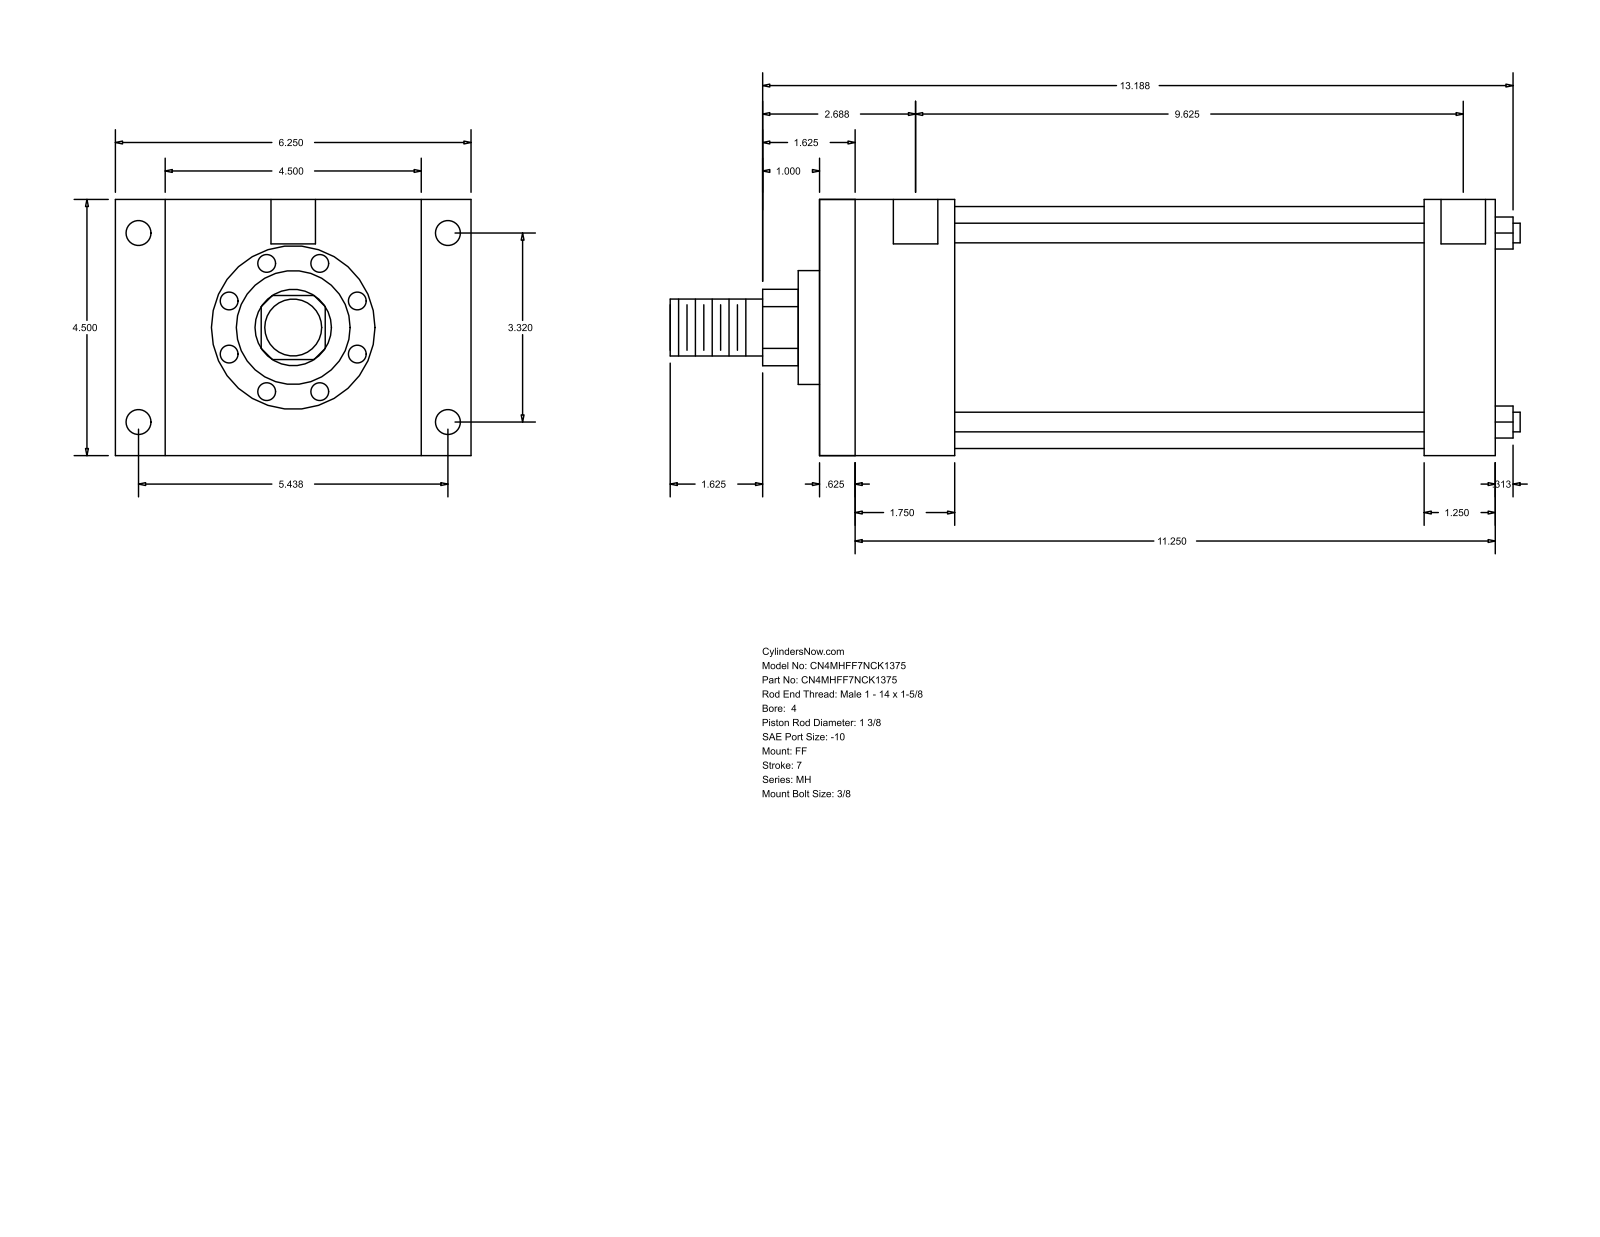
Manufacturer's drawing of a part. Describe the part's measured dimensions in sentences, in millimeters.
The part is named "MH_FF__0400_1.375". Its 3-D file was written by "GSSL Pune (CONFIG_CONTROL_DESIGN)". It is 0 solids with 92 faces: 64 planar, 28 cylindrical and 0 other. Overall it measures 379.41 by 158.75 by 114.3 millimeters. Round holes: 4 of diameter 8.73, 4 of diameter 11.13, 2 of diameter 19.84. Round bosses or shafts: 4 of diameter 8.76, 1 of diameter 107.95, 1 of diameter 50.8, 1 of diameter 34.92, 1 of diameter 25.4. Partial cylindrical surfaces (rounded edges, fillets, slot ends): 1 of radius 17.06. The main face-to-face distances are 114.3, 301.62, 15.87, 285.75, 60.32, 44.45, 241.3, 269.87, 254, 209.55. The hole center spacings are 84.32, 138.12, 161.82, 247.65, 1.58, 1.59, 244.48, 246.06.
